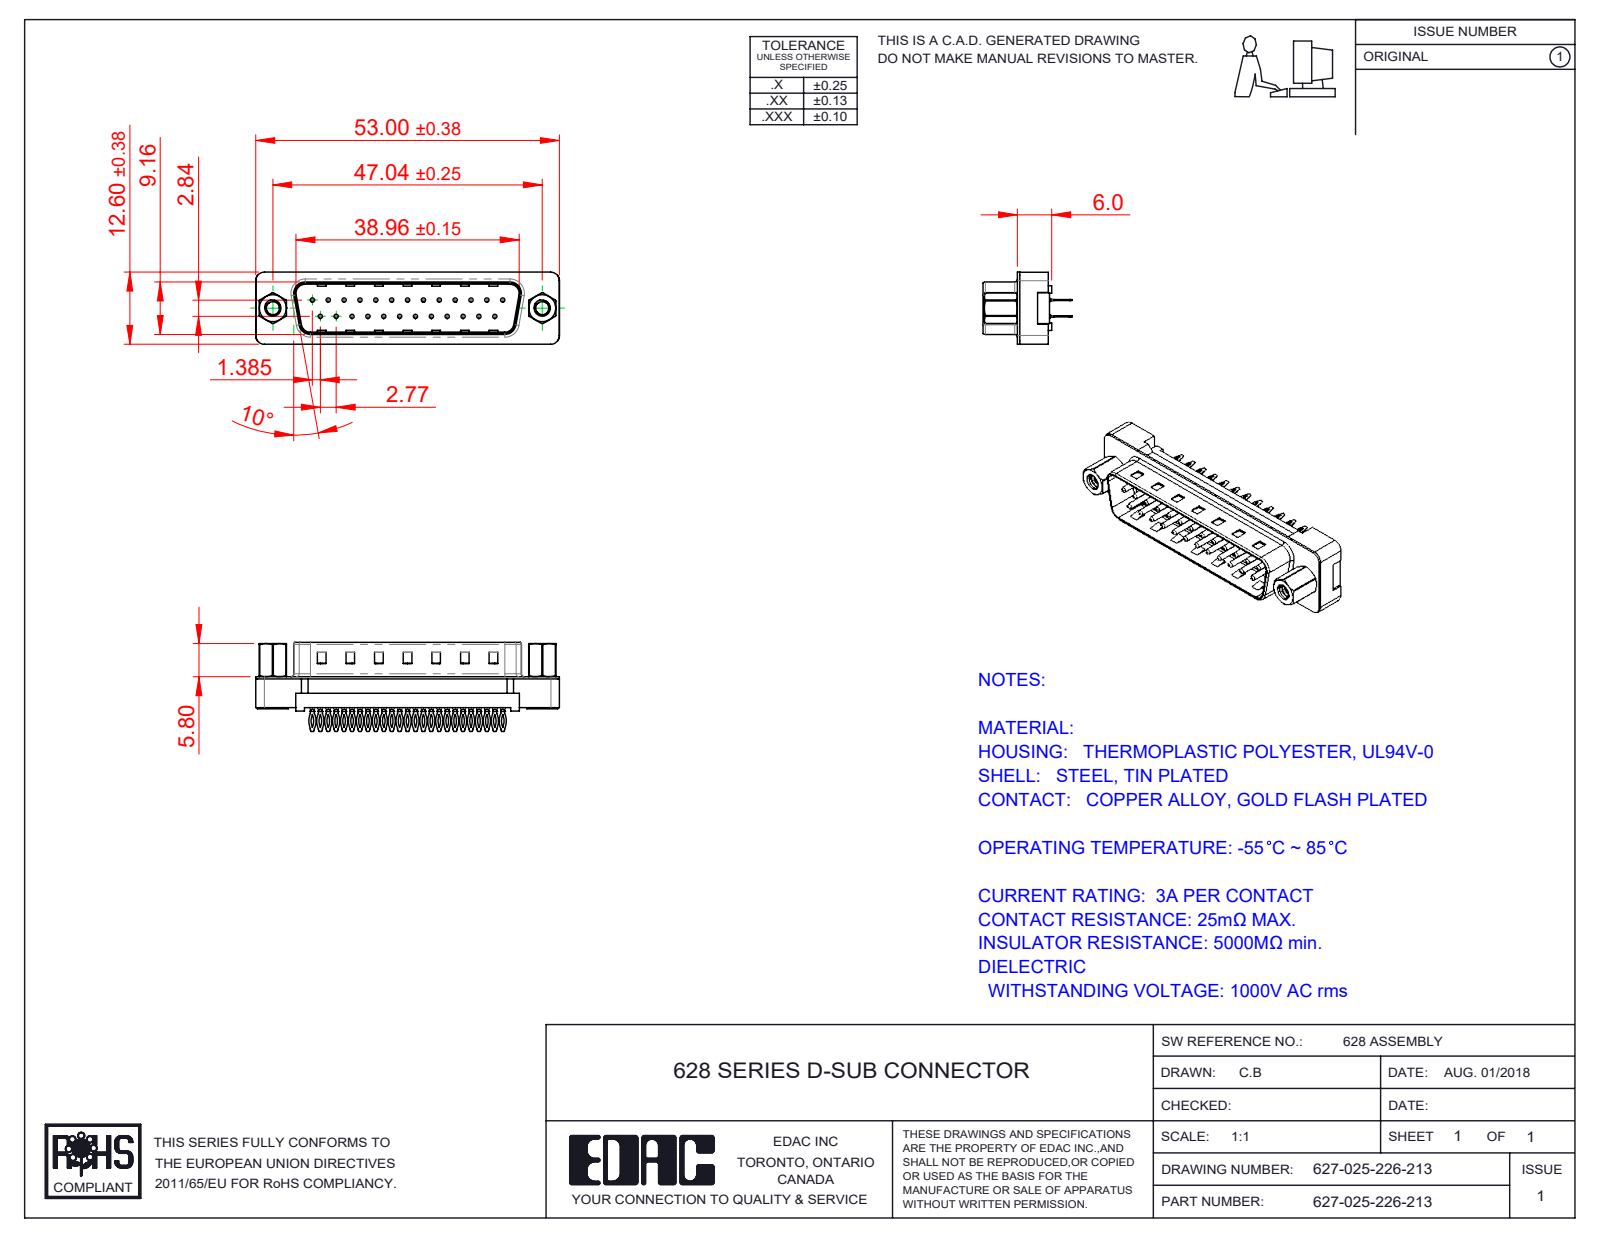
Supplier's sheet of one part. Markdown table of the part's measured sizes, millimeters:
| quantity | value |
| --- | --- |
| part name | 627 PB Contact Row 1_26; 627 PB Contact Row 2_26; 627 Plastic Body Housing_25 Contacts; 627 4-40 Hex Standoff (+3 more) |
| STEP written by | SolidWorks 2020 (CONFIG_CONTROL_DESIGN) |
| units | millimeters |
| bodies | 31 solids, 2218 faces (1300 planar, 676 cylindrical, 242 other) |
| overall size | 53.04 × 15.55 × 12.6 |
| volume | 2 750 mm³ |
| surface area | 6 261 mm² |
| round holes (diameter × count) | 0.35 × 25, 0.85 × 25, 2.26 × 2, 2.29 × 2, 4 × 2, 4.8 × 2, 5 × 2 |
| round bosses / shafts (diameter × count) | 0.75 × 25, 4.9 × 2, 2.79 × 2 |
| partial cylindrical surfaces (radius × count) | 0.25 × 50, 2.92 × 50, 3.33 × 50, 0.12 × 25, 0.5 × 8, 1.5 × 8, 0.9 × 4, 1.6 × 4 |
| main face-to-face distances | 0.4, 2.5, 8.76, 2.9, 5.4, 5, 1.3, 6.5, 8.48, 0.68 |
| hole center spacings | 3.16, 5.54, 2.77, 11.08, 8.31, 5.03, 13.85, 16.62 |
